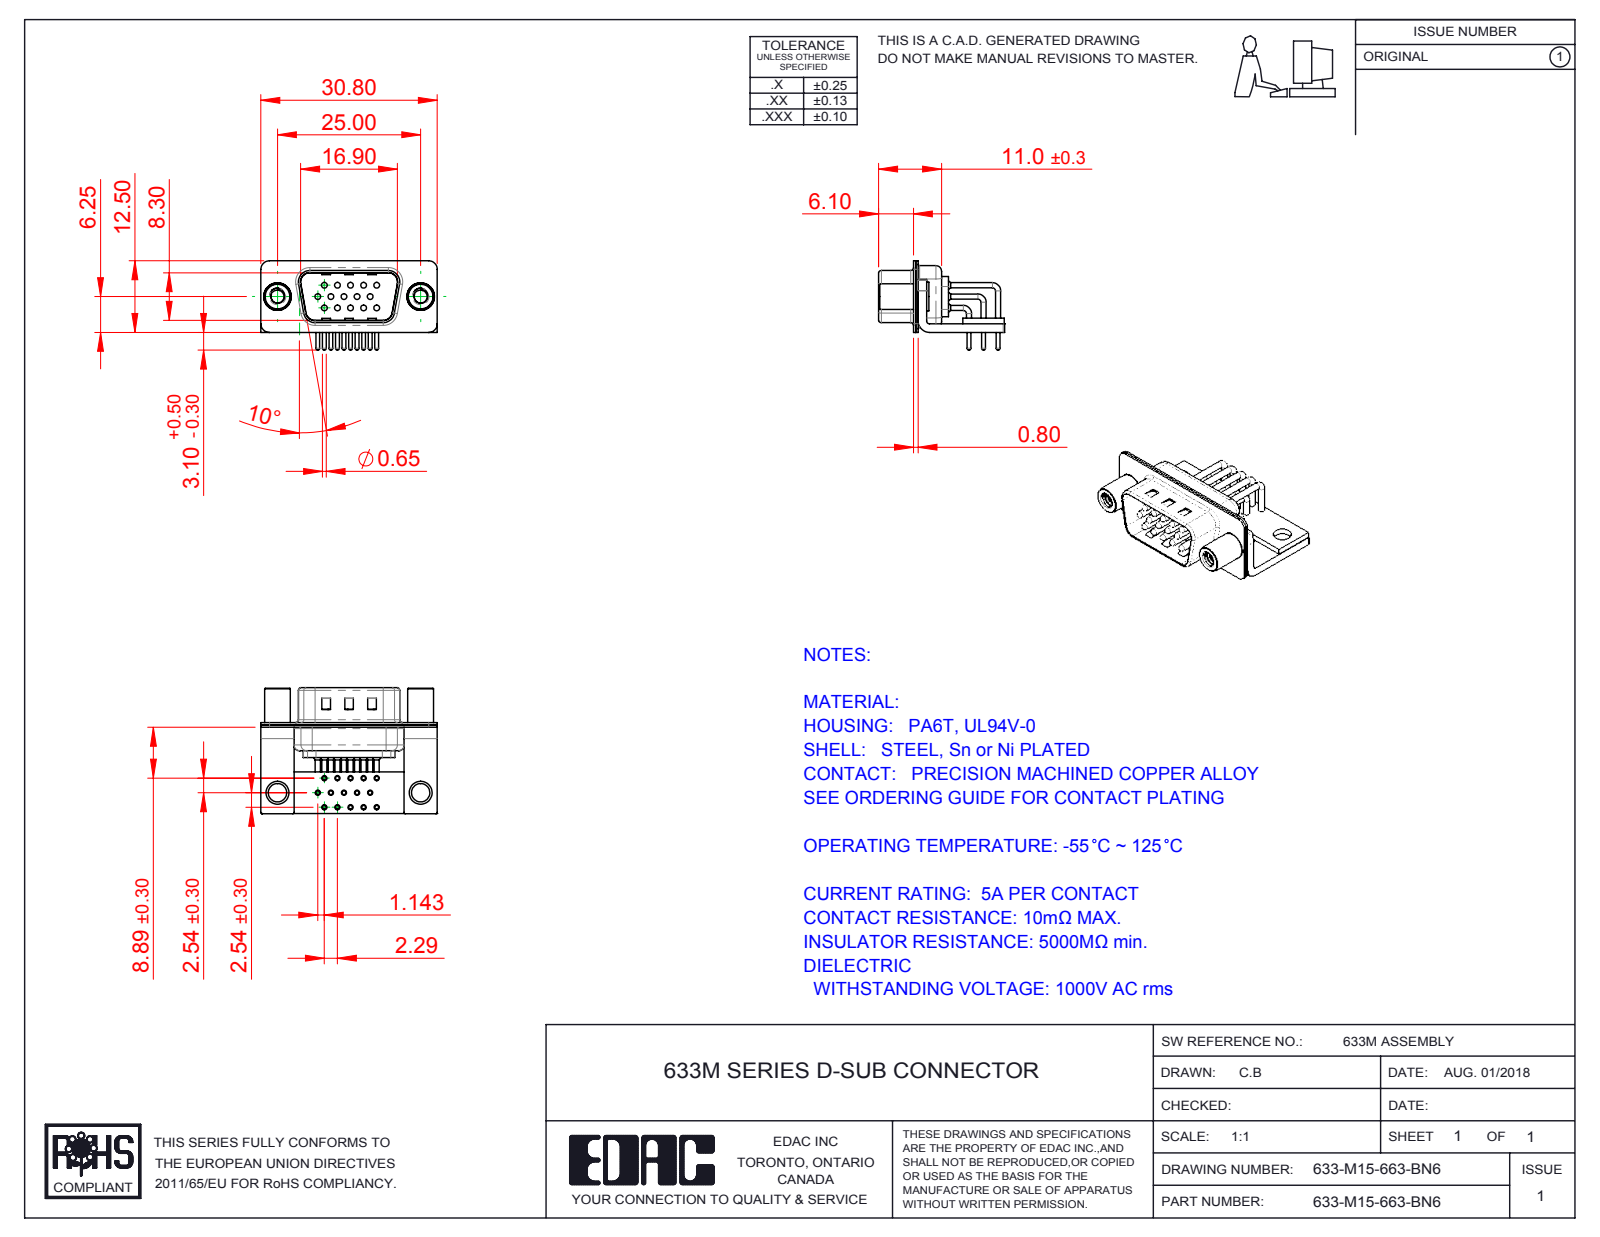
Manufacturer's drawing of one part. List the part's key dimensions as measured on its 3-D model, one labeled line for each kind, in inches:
Part name (STEP PRODUCT): 633-M15-663-BN6; 633M Stabilizer Board_15 Contacts; 633M 4-40 Threaded Standoff; 633M Stabilizer Bracket (+6 more)
STEP written by: SolidWorks 2016 (CONFIG_CONTROL_DESIGN)
Units: inches
Bodies: 23 solids, 2084 faces (1095 planar, 763 cylindrical, 226 other)
Overall size (bounding box): 1.213 × 0.866 × 0.614
Volume: 0.125 in³ · Surface area: 9.444 in²
Round holes (diameter × count): ⌀0.035 ×15, ⌀0.039 ×15, ⌀0.067 ×15, ⌀0.079 ×15, ⌀0.089 ×2, ⌀0.126 ×2, ⌀0.157 ×2, ⌀0.189 ×2
Round bosses / shafts (diameter × count): ⌀0.035 ×16, ⌀0.059 ×15, ⌀0.026 ×15, ⌀0.197 ×2, ⌀0.193 ×2, ⌀0.177 ×2
Partial cylindrical surfaces — rounded edges, fillets, slot ends (radius × count): R0.01 ×16, R0.059 ×16, R0.04 ×15, R0.079 ×13, R0.02 ×9, R0.063 ×8, R0.024 ×4, R0.026 ×4
Main face-to-face distances: 0.016, 0.059, 0.031, 0.039, 0.033, 0.075, 0.049, 0.098, 0.409, 0.376
Hole centre spacings: 0.09, 0.18, 0.09, 0.156, 0.109, 0.168, 0.238, 0.27
